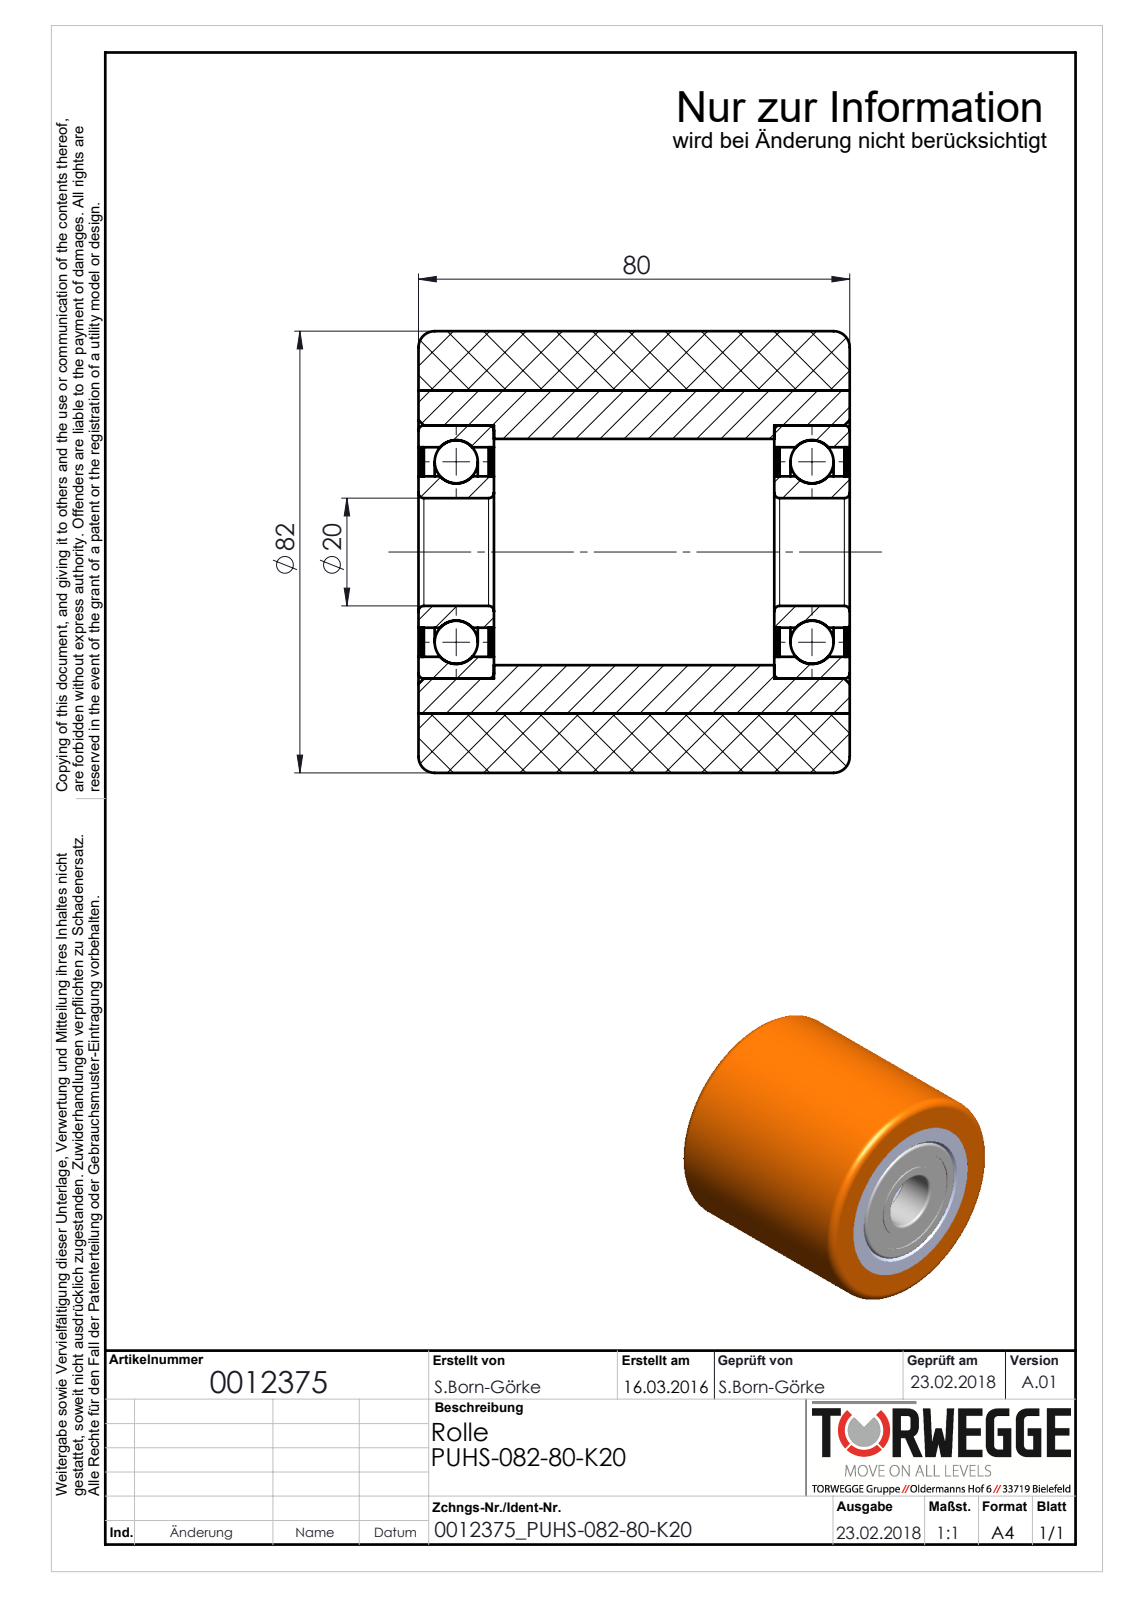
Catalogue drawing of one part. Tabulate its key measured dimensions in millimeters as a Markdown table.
| quantity | value |
| --- | --- |
| part name | 0012375_PUHS-082-80-K20 |
| STEP written by | SolidWorks 2016 (AUTOMOTIVE_DESIGN) |
| units | millimeters |
| bodies | 12 solids, 118 faces (22 planar, 52 cylindrical, 44 other) |
| overall size | 82 × 82 × 80 |
| volume | 333 615 mm³ |
| surface area | 94 149 mm² |
| round holes (diameter × count) | 20 × 1, 28.1 × 1, 38.9 × 1, 42 × 1, 47 × 1, 60 × 1 |
| round bosses / shafts (diameter × count) | 82 × 1 |
| main face-to-face distances | 0.5, 66, 13, 80, 1, 13.5, 66.5, 12.5, 65.5, 14 |
